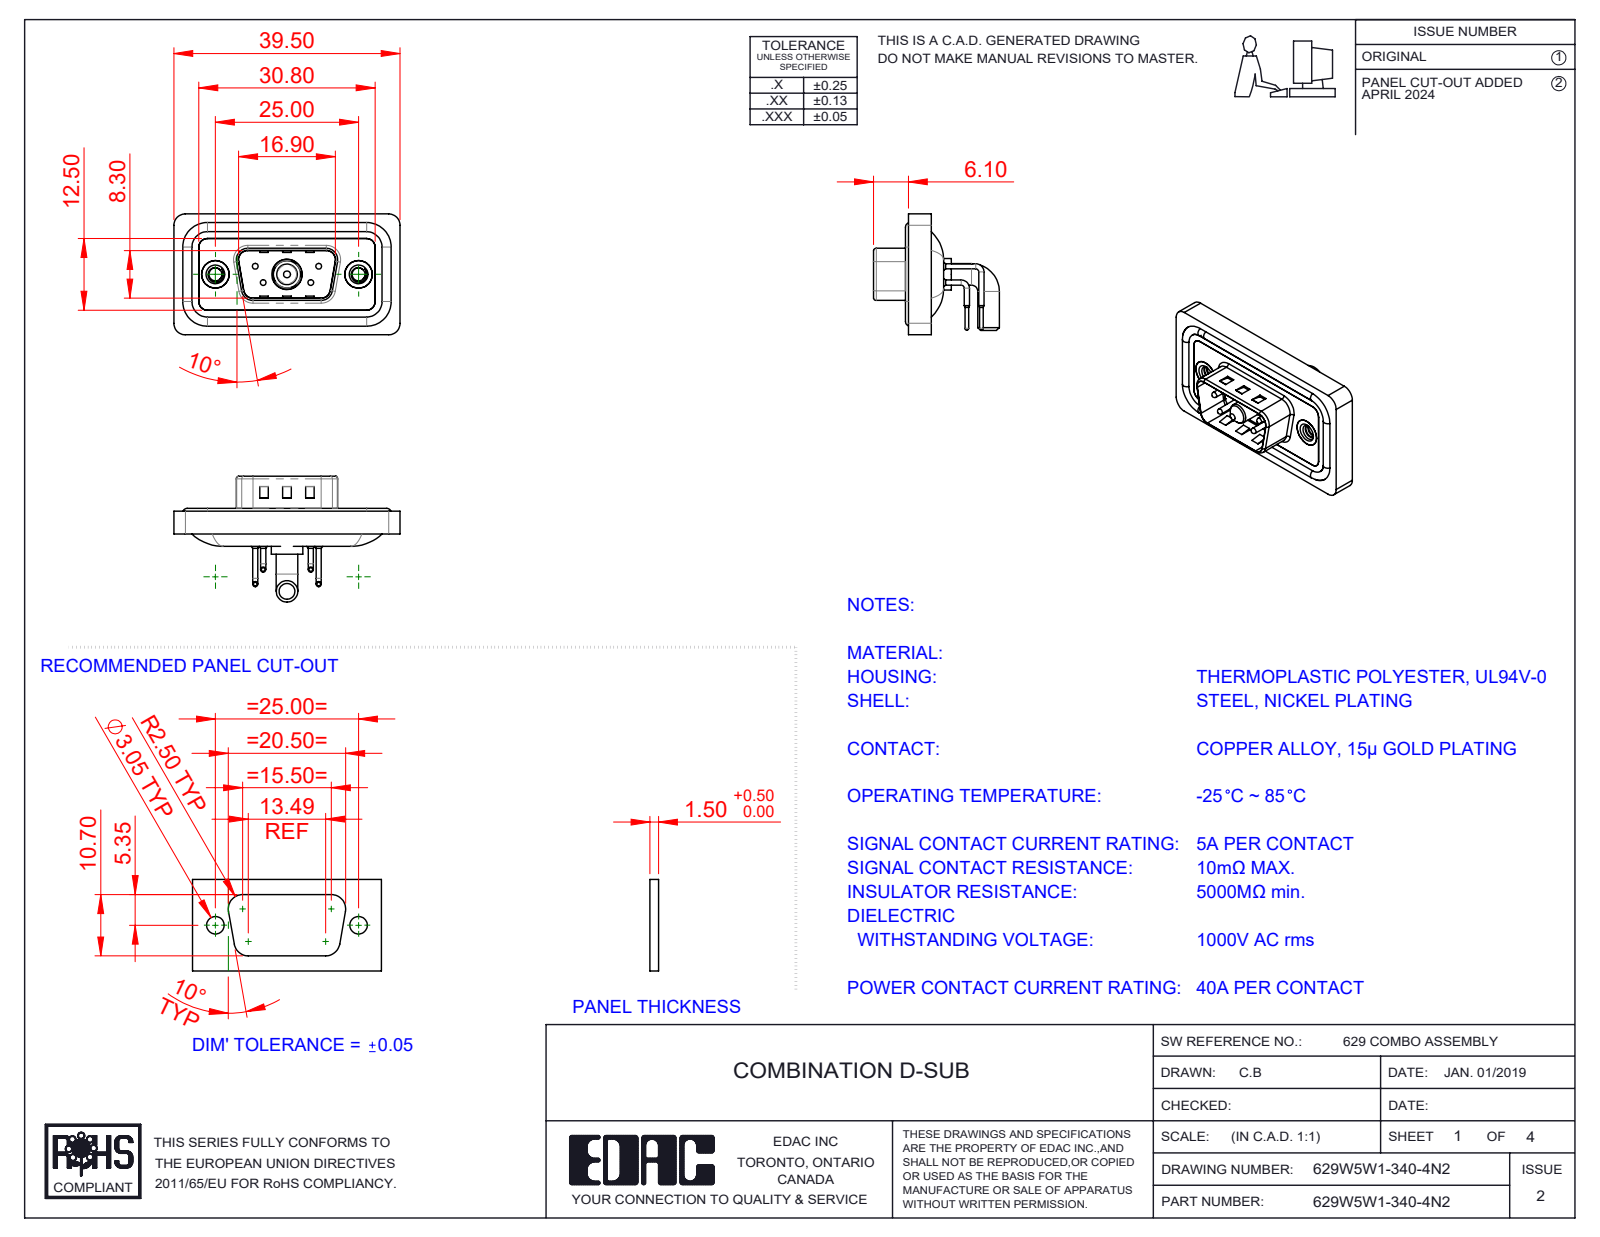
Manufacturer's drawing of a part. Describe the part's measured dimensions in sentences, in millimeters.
The part is named "629Combo Shell Front_09 Contacts; 629W5W1-340-4N2; Power Pin_40A RA; 629Combo Threaded Rivet_2 (+5 more)". Its 3-D file was written by "SolidWorks 2023 (CONFIG_CONTROL_DESIGN)". It is 13 solids with 894 faces: 411 planar, 345 cylindrical and 138 other. Overall it measures 39.5 by 21.98 by 21.1 millimeters. Its volume is 4 560 cubic millimeters and its surface area 7 208 square millimeters. Round holes: 4 of diameter 0.75, 4 of diameter 1.6, 4 of diameter 2, 2 of diameter 2.26, 2 of diameter 4, 2 of diameter 4.8, 2 of diameter 5, 1 of diameter 4.85, 1 of diameter 5.3. Round bosses or shafts: 8 of diameter 0.9, 4 of diameter 1.6, 4 of diameter 1.5, 4 of diameter 1, 4 of diameter 0.65, 2 of diameter 4.9, 2 of diameter 3.75, 1 of diameter 5.5. Partial cylindrical surfaces (rounded edges, fillets, slot ends): 18 of radius 1.5, 18 of radius 2, 8 of radius 0.5, 8 of radius 1.6, 4 of radius 0.25, 4 of radius 0.6, 4 of radius 0.65, 4 of radius 0.9. The main face-to-face distances are 0.4, 2.9, 1.1, 0.8, 2.1, 2.5, 1.6, 3.1, 4.5, 1.5. The hole center spacings are 3.16, 5.72, 7.1, 12.5, 18.1, 4.39, 4.4, 8.31.
